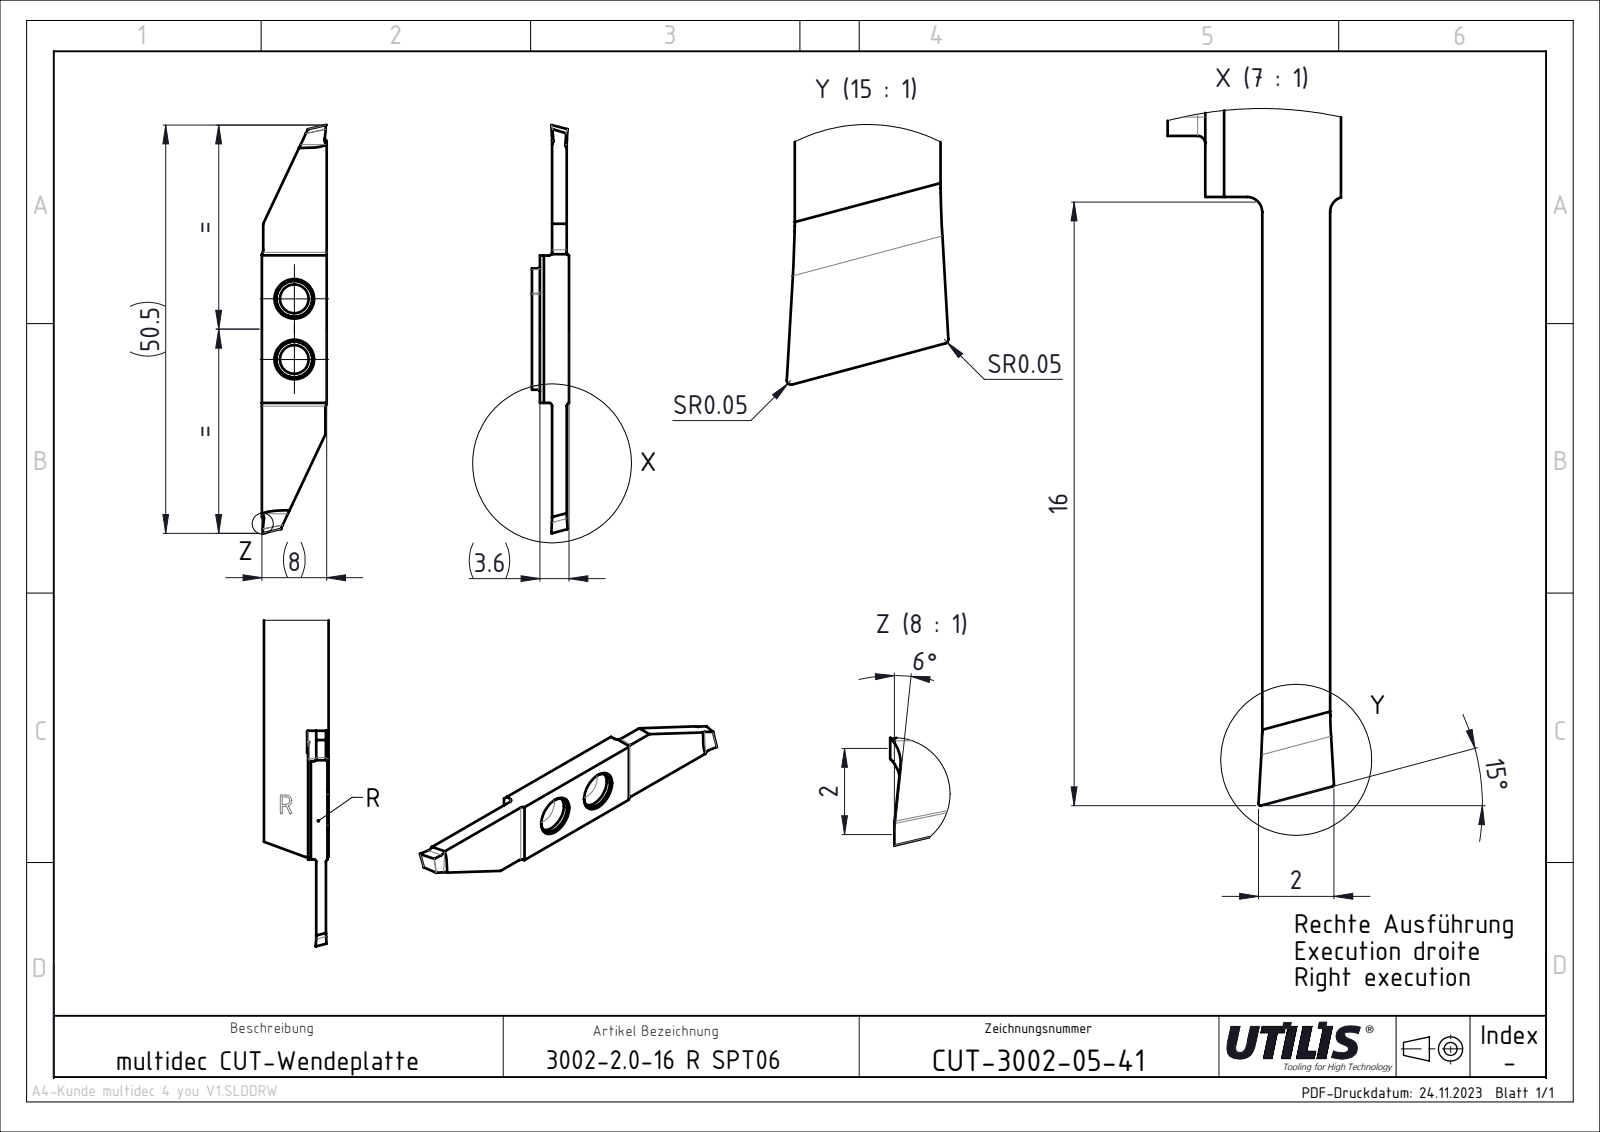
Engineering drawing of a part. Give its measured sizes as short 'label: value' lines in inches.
name: CUT-3002 SPT Slim_and_Deep; ASME Y14.5
written by: SolidWorks 2023 SP4 || FormatWorks Professional (AP242_MANAGED_MODEL_BASED_3D_ENGINEERING_MIM_LF)
unit: in
bodies: 1 solid, 36 faces (22 planar, 14 cylindrical, 0 other)
size: 1.988 × 0.315 × 0.142
volume: 0.048 in³; area: 1.5 in²
holes: 2× ⌀0.14
rounds: 4× R0.016, 2× R0.039
face distances: 0.071, 0.082, 0.059, 0.13, 0.142, 0.315, 0.712, 0.309, 0.717, 0.303
hole spacings: 0.295
